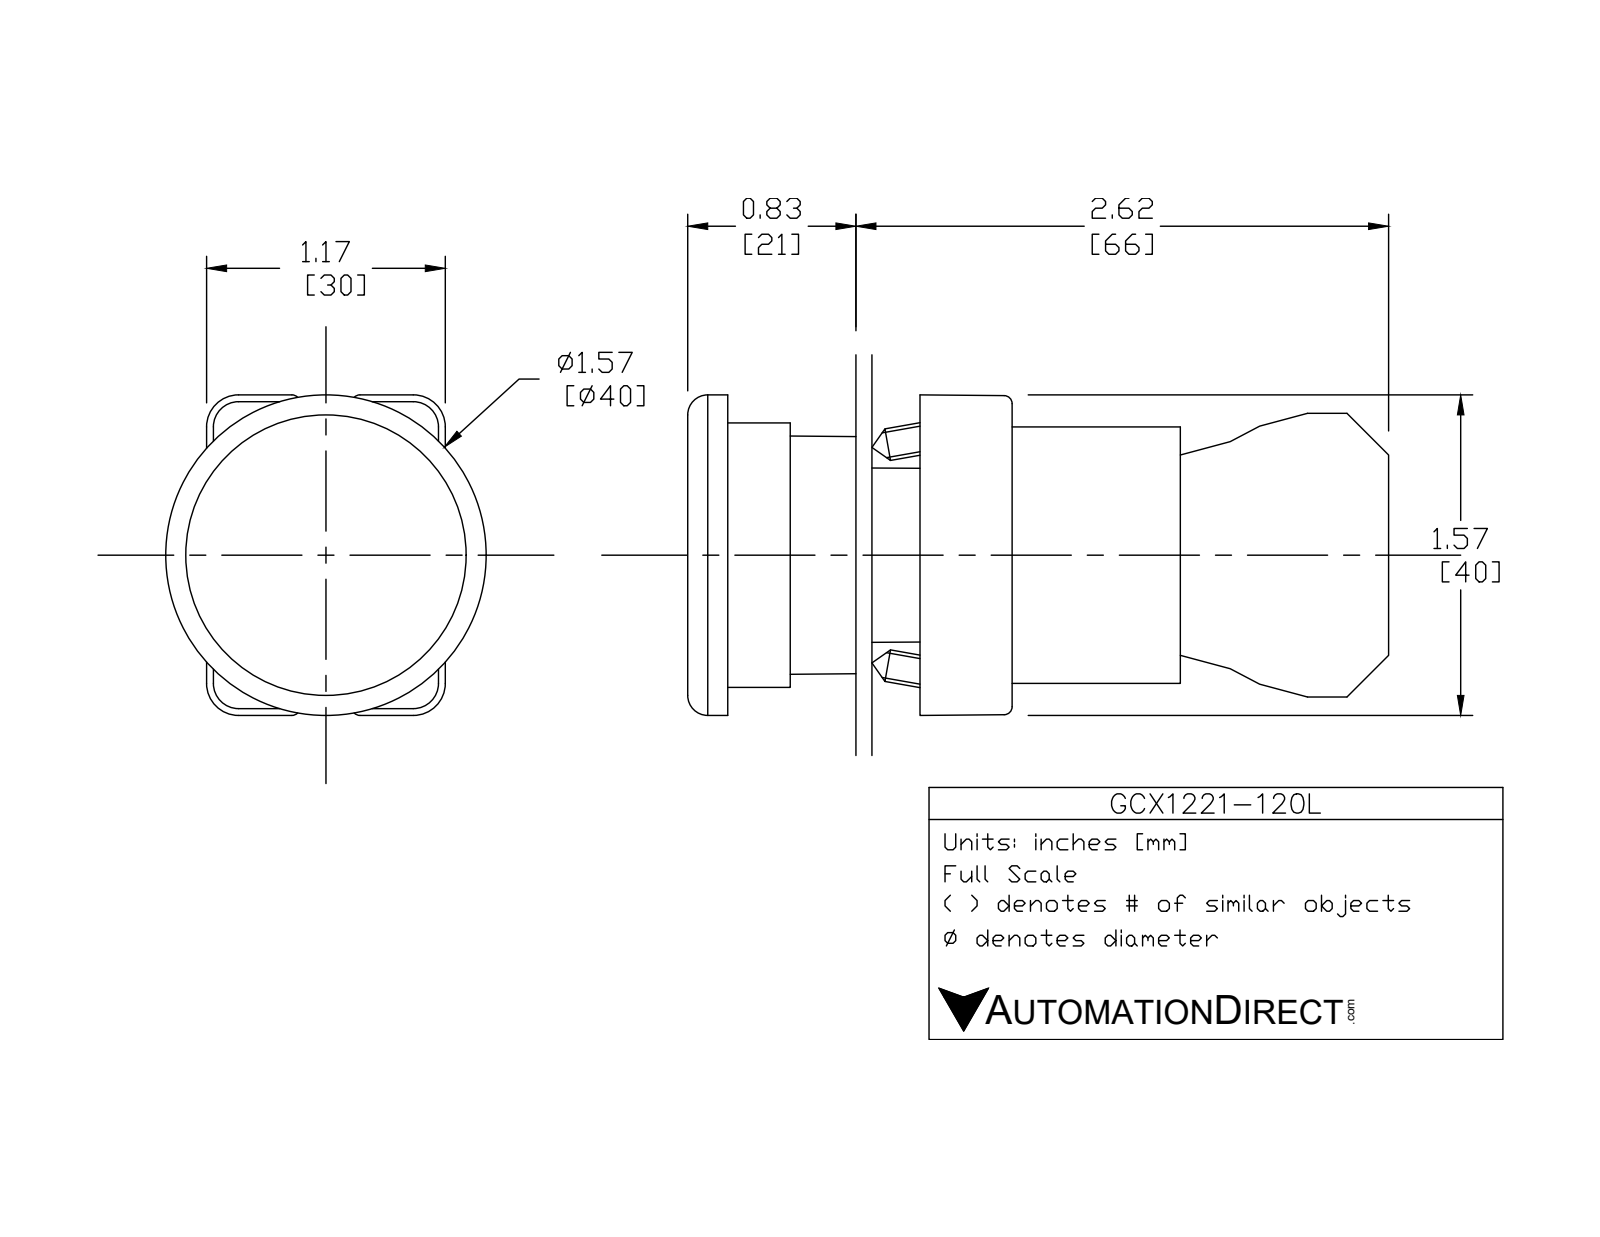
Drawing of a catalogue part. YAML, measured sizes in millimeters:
part_name: "ecx1030; GCX1221-120L; ECX1029-2; ECX1050 (+1 more)"
step_written_by: "SolidWorks 2016 (AUTOMOTIVE_DESIGN)"
units: millimeters
bodies: {solids: 7, faces: 431, planar: 252, cylindrical: 146, other: 33}
overall_size: [88.1, 40.2, 40]
volume: 47440
surface_area: 26380
round_holes:
  - {diameter: 2, count: 2}
  - {diameter: 3.1, count: 2}
  - {diameter: 3.3, count: 2}
  - {diameter: 2.2, count: 1}
  - {diameter: 5, count: 1}
  - {diameter: 11.9, count: 1}
  - {diameter: 22.3, count: 1}
  - {diameter: 22.6, count: 1}
  - {diameter: 26, count: 1}
  - {diameter: 30, count: 1}
round_bosses_or_shafts:
  - {diameter: 4, count: 4}
  - {diameter: 33, count: 1}
  - {diameter: 29.8, count: 1}
  - {diameter: 24, count: 1}
  - {diameter: 21.7, count: 1}
  - {diameter: 19.8, count: 1}
  - {diameter: 12.8, count: 1}
partial_cylinders:
  - {radius: 1.5, count: 24}
  - {radius: 1, count: 12}
  - {radius: 3.1, count: 12}
  - {radius: 4, count: 12}
  - {radius: 1, count: 8}
  - {radius: 3.3, count: 2}
  - {radius: 0.5, count: 1}
  - {radius: 1.6, count: 1}
face_to_face_distances: [21, 62.1, 41.1, 14.7, 58.1, 37.1, 4, 14.9, 0.8, 29.6]
hole_center_spacings: [6, 13.7, 12, 12.3]
